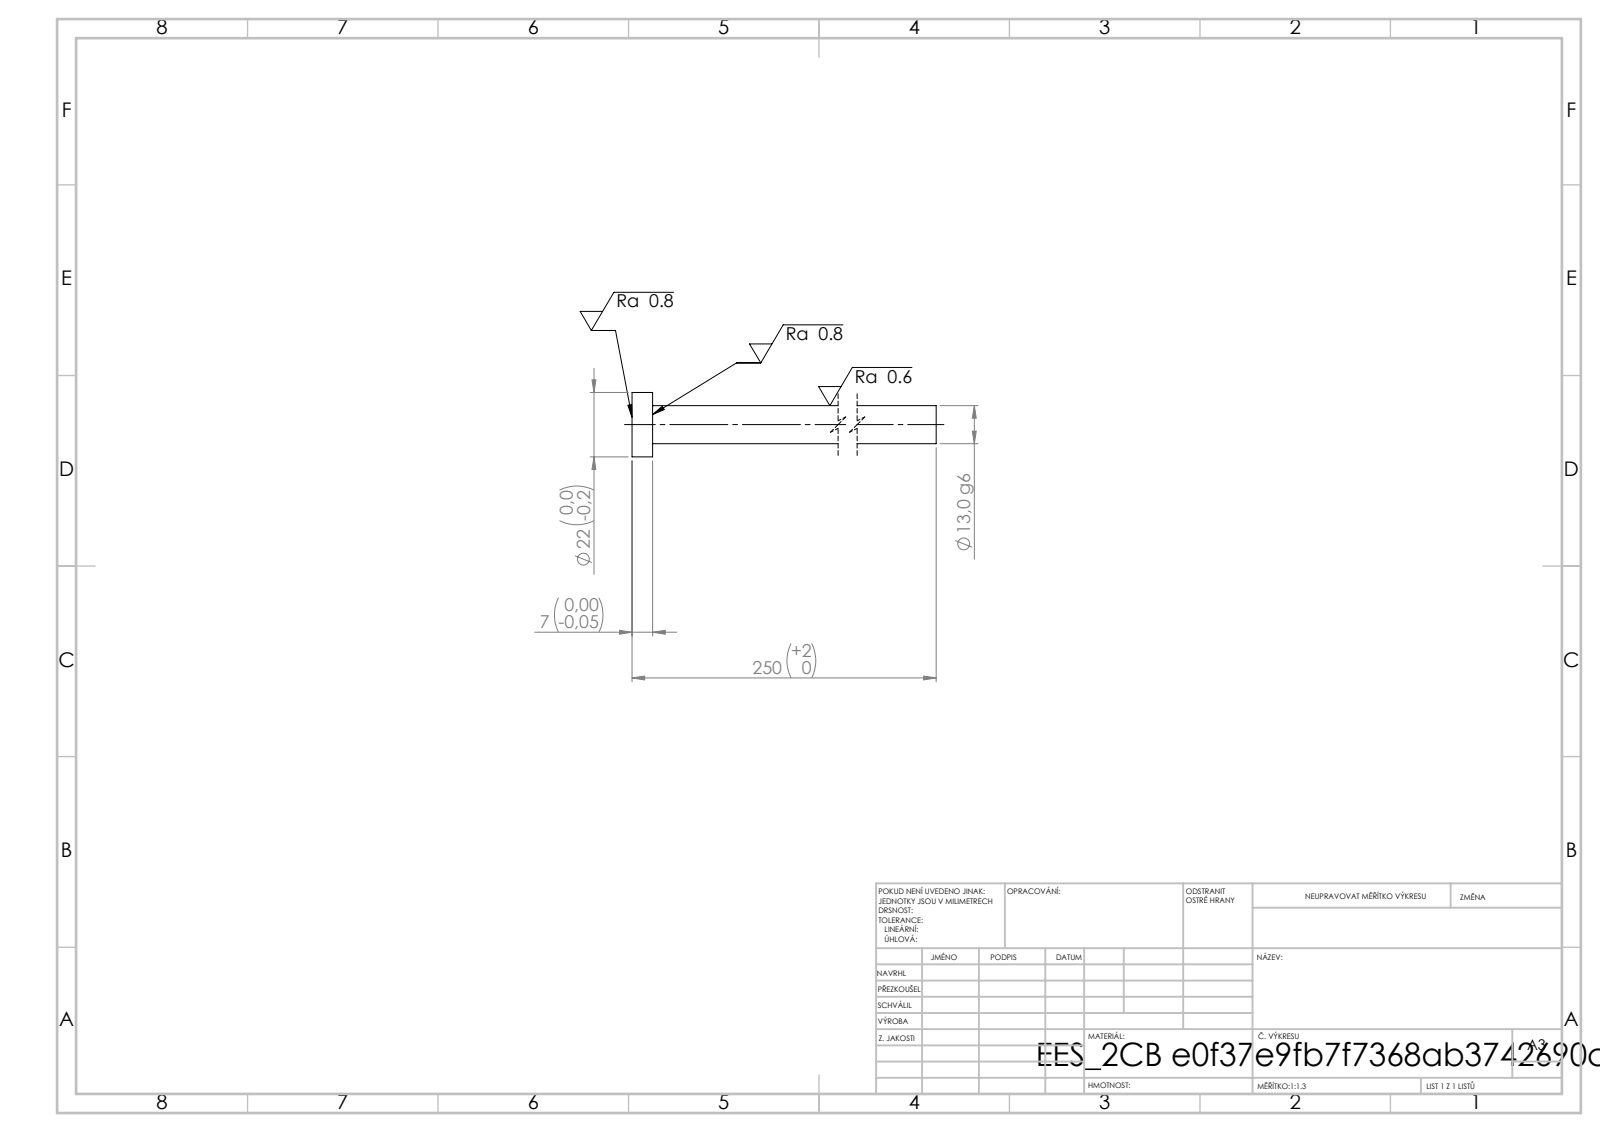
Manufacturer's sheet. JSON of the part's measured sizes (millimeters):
{"step_written_by": "SolidWorks 2019 (CONFIG_CONTROL_DESIGN)", "units": "millimeters", "bodies": {"solids": 1, "faces": 7, "planar": 3, "cylindrical": 4, "other": 0}, "overall_size": [250, 22, 22], "volume_mm3": 34915, "surface_area_mm2": 11168, "round_bosses_or_shafts": [[22, 1], [13, 1]], "face_to_face_distances": [7, 250, 243]}
